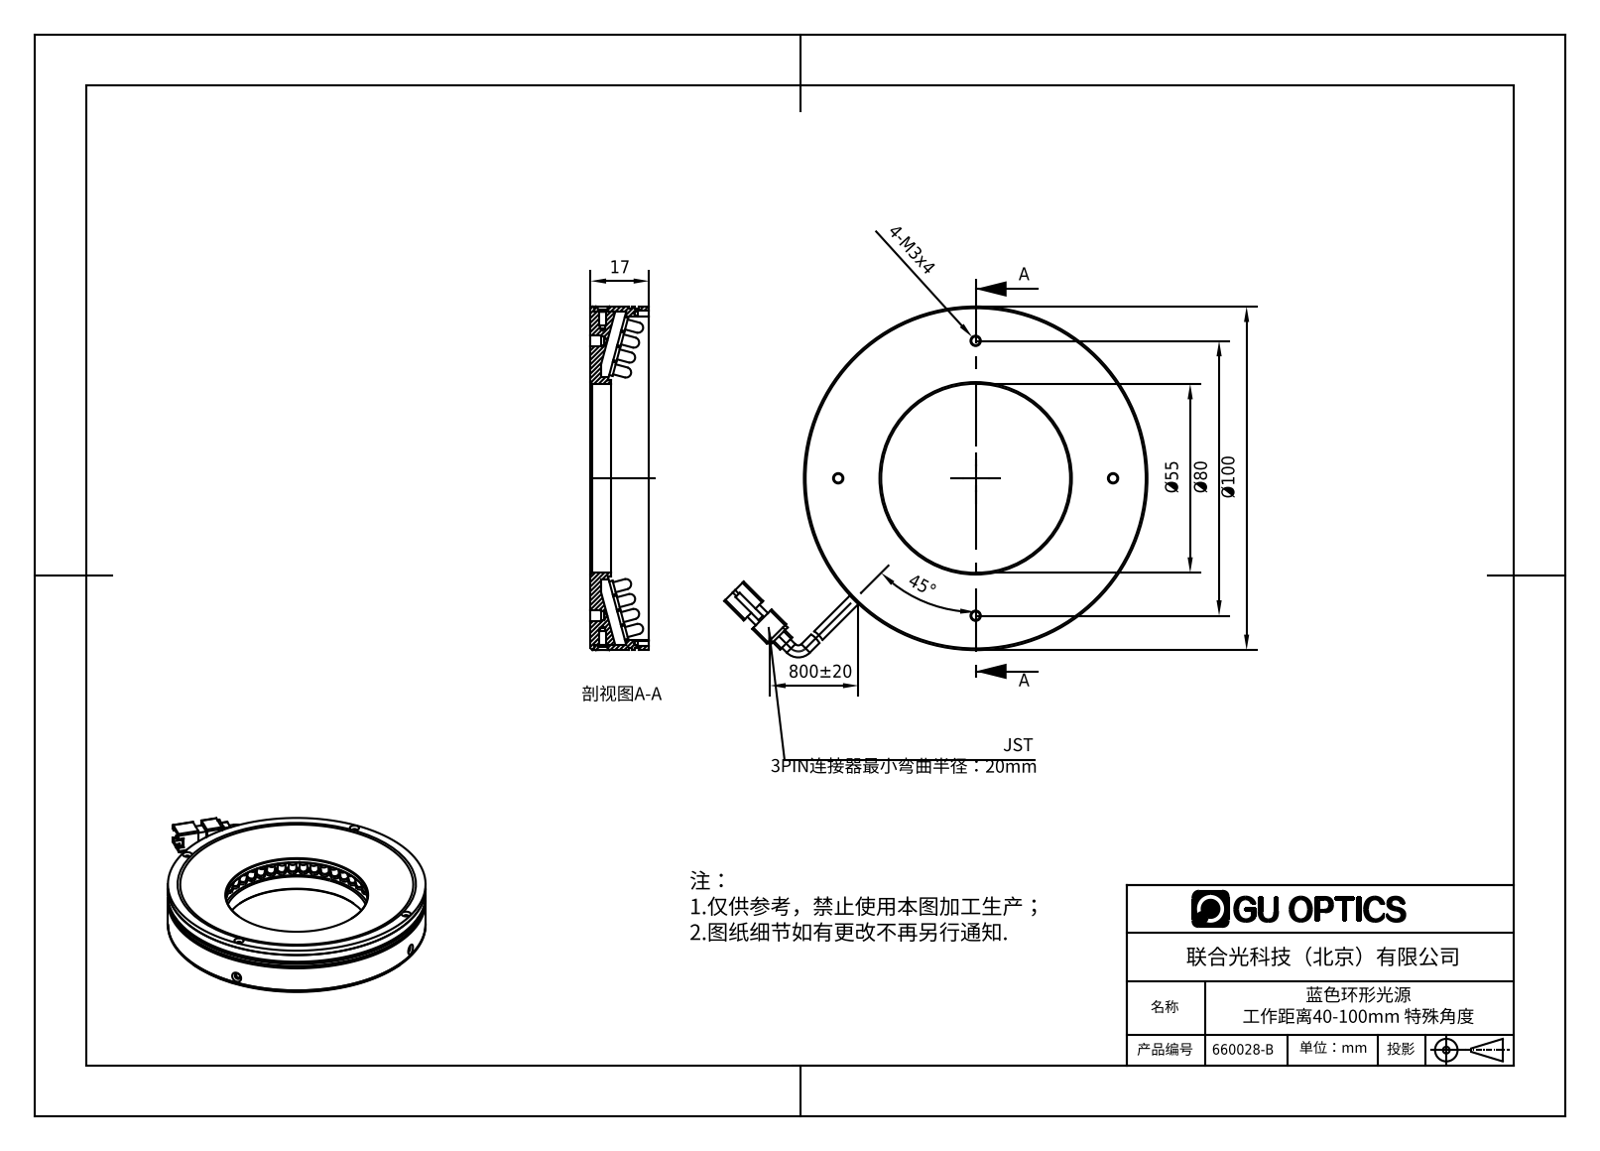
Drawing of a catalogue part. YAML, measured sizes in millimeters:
part_name: "660028-B"
step_written_by: "SolidWorks 2016 (AUTOMOTIVE_DESIGN)"
units: millimeters
bodies: {solids: 216, faces: 3870, planar: 2609, cylindrical: 980, other: 281}
overall_size: [123.19, 102.13, 22.45]
volume: 58180
surface_area: 68815
round_holes:
  - {diameter: 1.6, count: 6}
  - {diameter: 1.25, count: 4}
  - {diameter: 1.7, count: 4}
  - {diameter: 2.5, count: 4}
  - {diameter: 3, count: 4}
  - {diameter: 3.5, count: 4}
  - {diameter: 2, count: 2}
  - {diameter: 2.4, count: 2}
  - {diameter: 55, count: 1}
  - {diameter: 94, count: 1}
round_bosses_or_shafts:
  - {diameter: 3.8, count: 210}
  - {diameter: 3, count: 210}
  - {diameter: 3.5, count: 2}
  - {diameter: 100, count: 1}
  - {diameter: 99, count: 1}
  - {diameter: 97, count: 1}
  - {diameter: 59, count: 1}
  - {diameter: 57, count: 1}
partial_cylinders:
  - {radius: 0.5, count: 10}
  - {radius: 1, count: 4}
  - {radius: 1.65, count: 1}
  - {radius: 7.5, count: 1}
face_to_face_distances: [1, 2, 17, 3, 16, 0.5, 19, 14, 18, 5]
hole_center_spacings: [62.48, 8, 40, 48, 56.57, 67.88, 88, 80]
